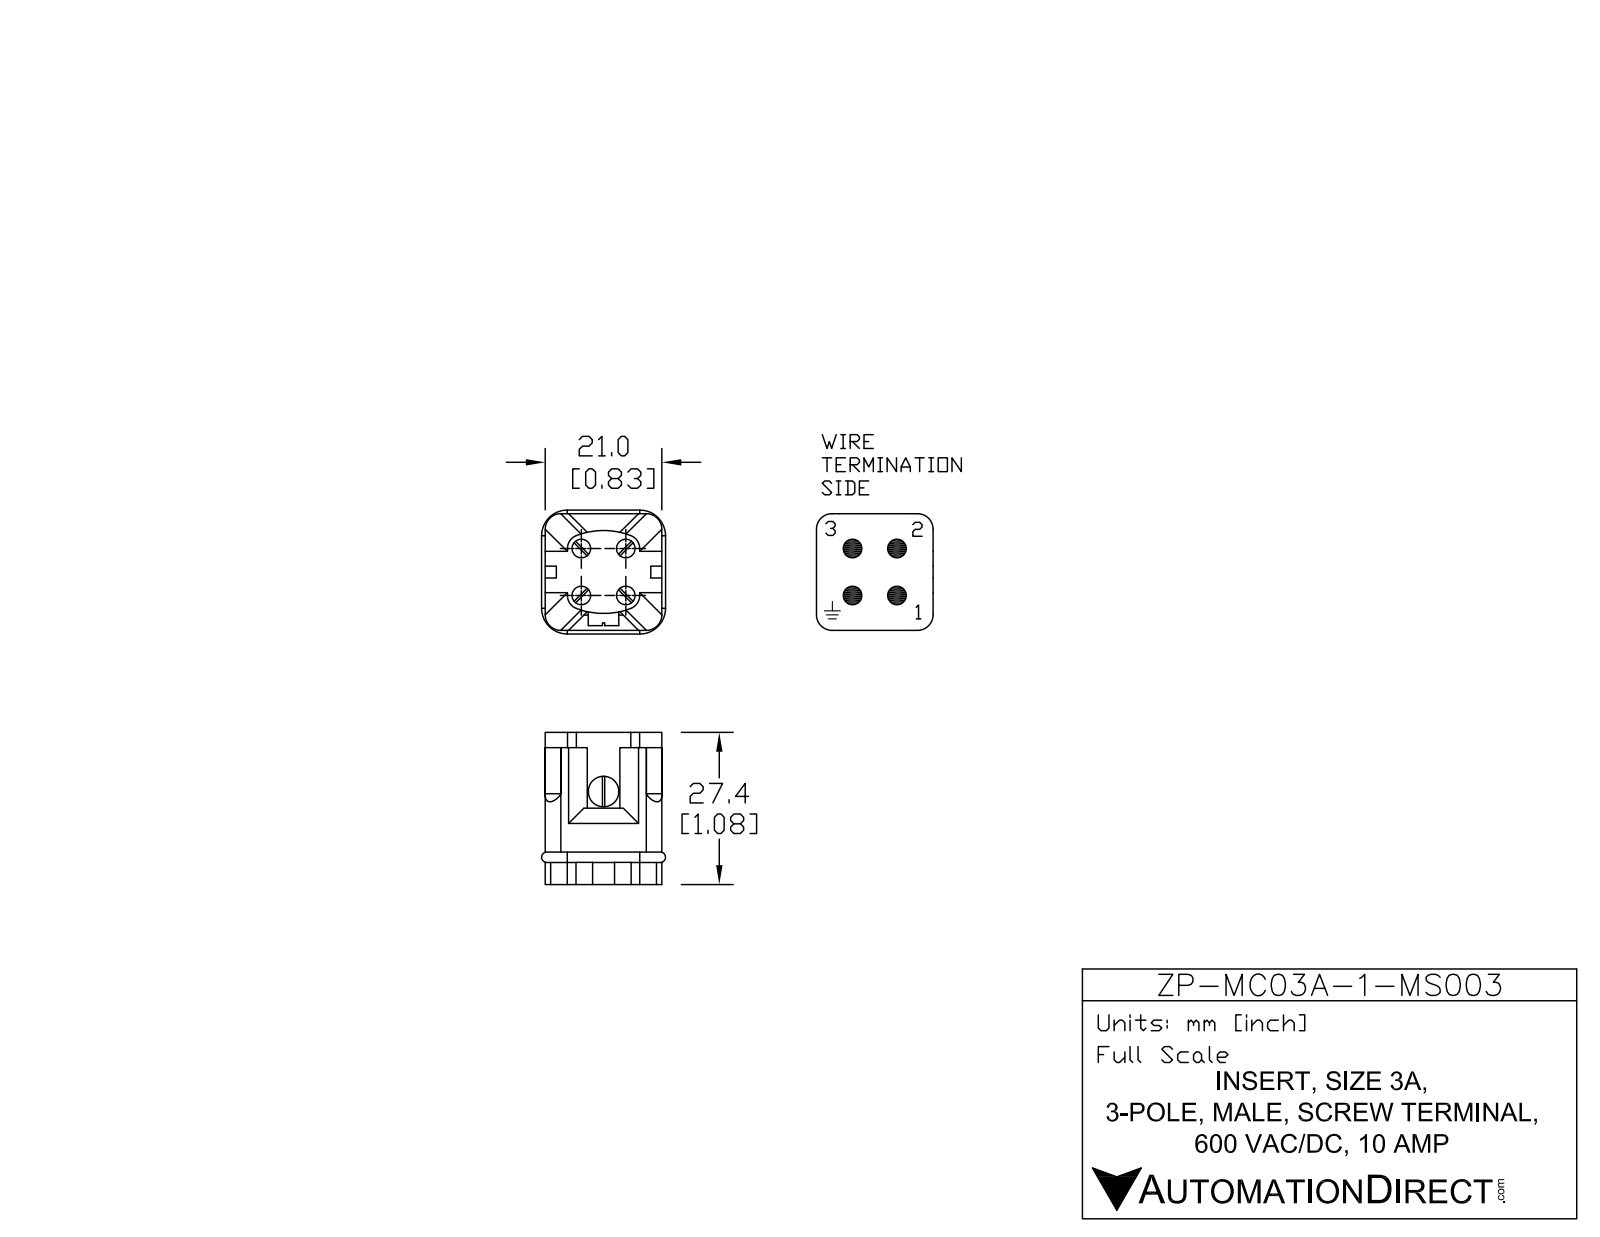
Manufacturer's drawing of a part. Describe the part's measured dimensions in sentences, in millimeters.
The part is named "ZP-3A-3-MS-INSERT". Its 3-D file was written by "SolidWorks 2011 (AUTOMOTIVE_DESIGN)". It is 1 solid with 170 faces: 118 planar, 44 cylindrical and 8 other. Overall it measures 27.4 by 22.31 by 22.31 millimeters. Its volume is 7 170 cubic millimeters and its surface area 4 741 square millimeters. Round holes: 4 of diameter 3.35. Round bosses or shafts: 4 of diameter 1.6, 1 of diameter 5.5. Partial cylindrical surfaces (rounded edges, fillets, slot ends): 4 of radius 0.9, 4 of radius 0.95, 4 of radius 2.5, 4 of radius 2.8, 4 of radius 3, 2 of radius 2.06, 2 of radius 13.65, 1 of radius 1.26. The main face-to-face distances are 21, 3.08, 17.92, 1, 4.94, 3.94, 15.55, 27.4, 11.85, 3.07. The hole center spacings are 8, 8.44, 11.63.
